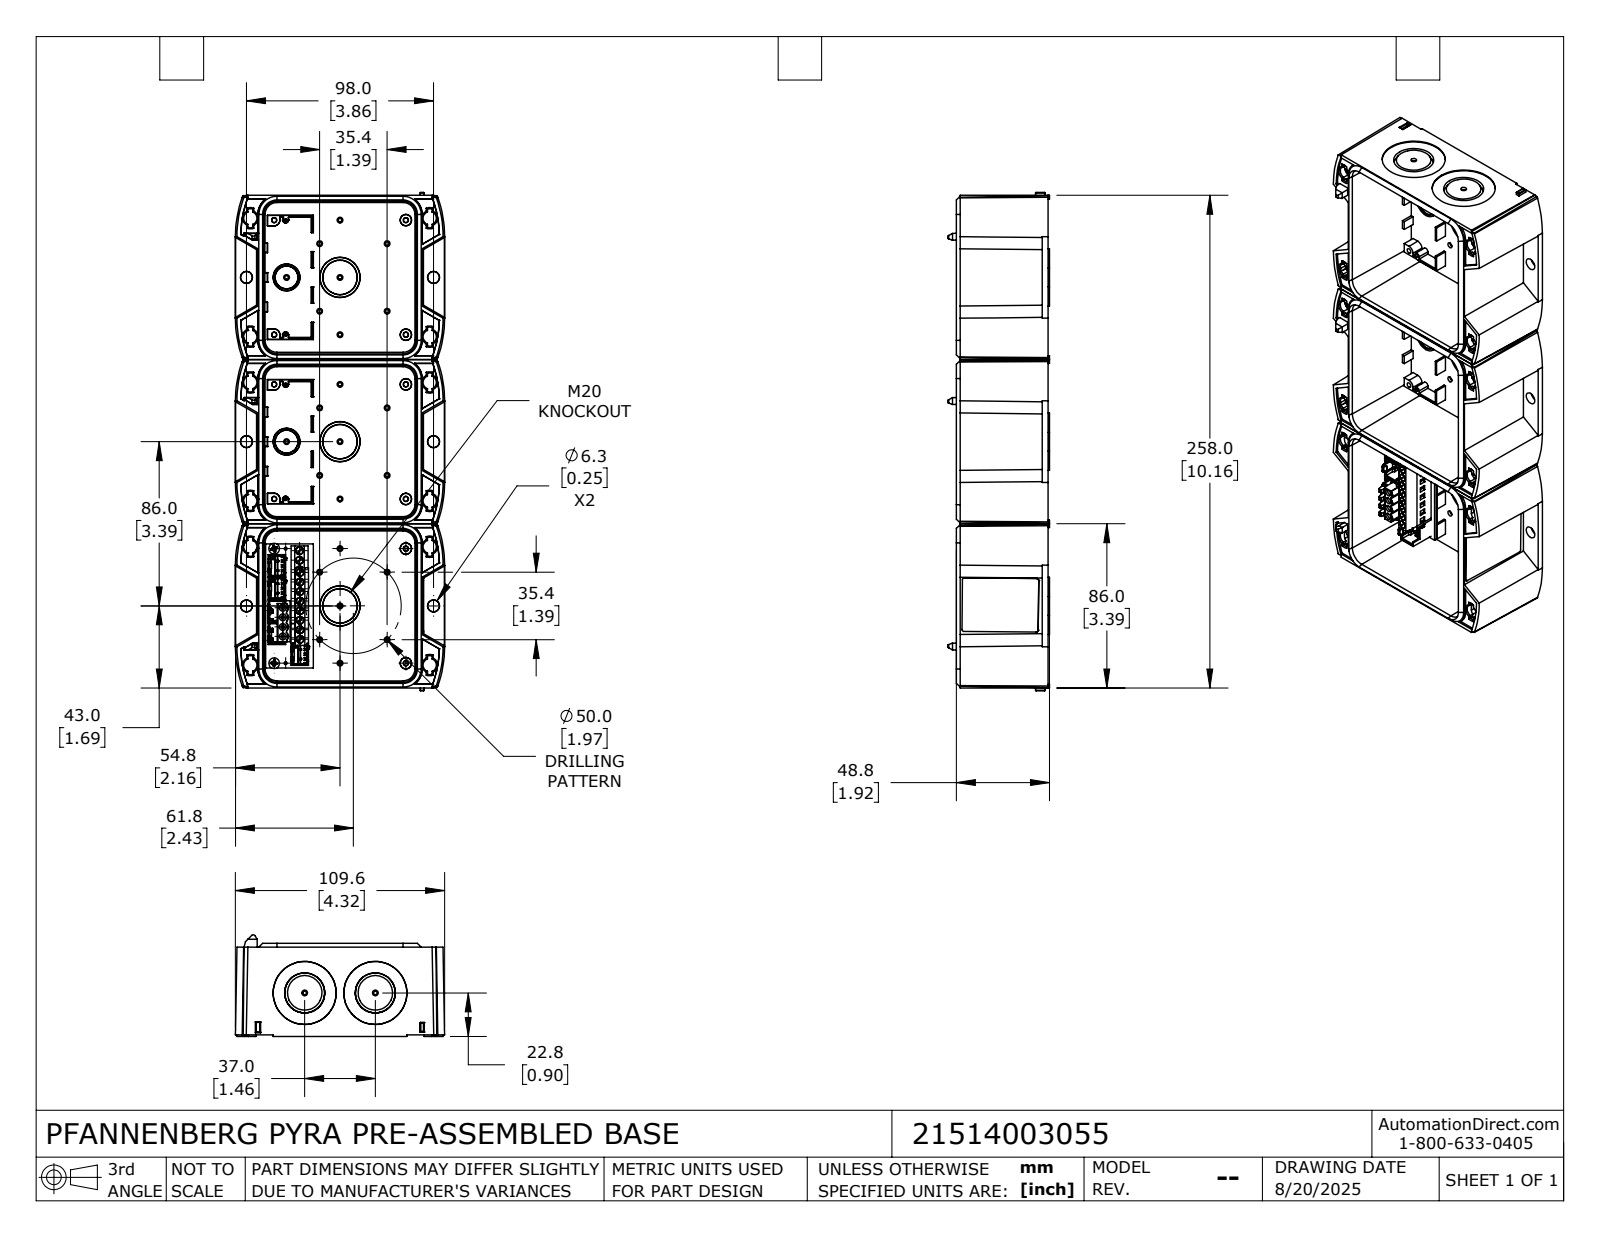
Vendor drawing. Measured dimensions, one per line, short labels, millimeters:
name: 21514003055
written by: SolidWorks 2024 (CONFIG_CONTROL_DESIGN)
unit: mm
bodies: 19 solids, 3300 faces (2218 planar, 407 cylindrical, 675 other)
size: 261 × 109.61 × 53.28
volume: 290 943 mm³; area: 221 102 mm²
holes: 18× ⌀4, 10× ⌀1, 10× ⌀1.4, 5× ⌀1.9, 4× ⌀1.8, 4× ⌀2.3, 4× ⌀3.6, 2× ⌀1.5, 2× ⌀3
bosses: 18× ⌀3.8, 5× ⌀1.8, 2× ⌀5.6, 2× ⌀2.9
rounds: 48× R0.3, 15× R1, 14× R0.4, 10× R0.5, 5× R2.9, 3× R9
face distances: 86, 3, 172, 83, 85.5, 0.5, 74.48, 171.5, 6.5, 9.5
hole spacings: 5, 10, 15, 11, 16, 20, 21, 6.01
